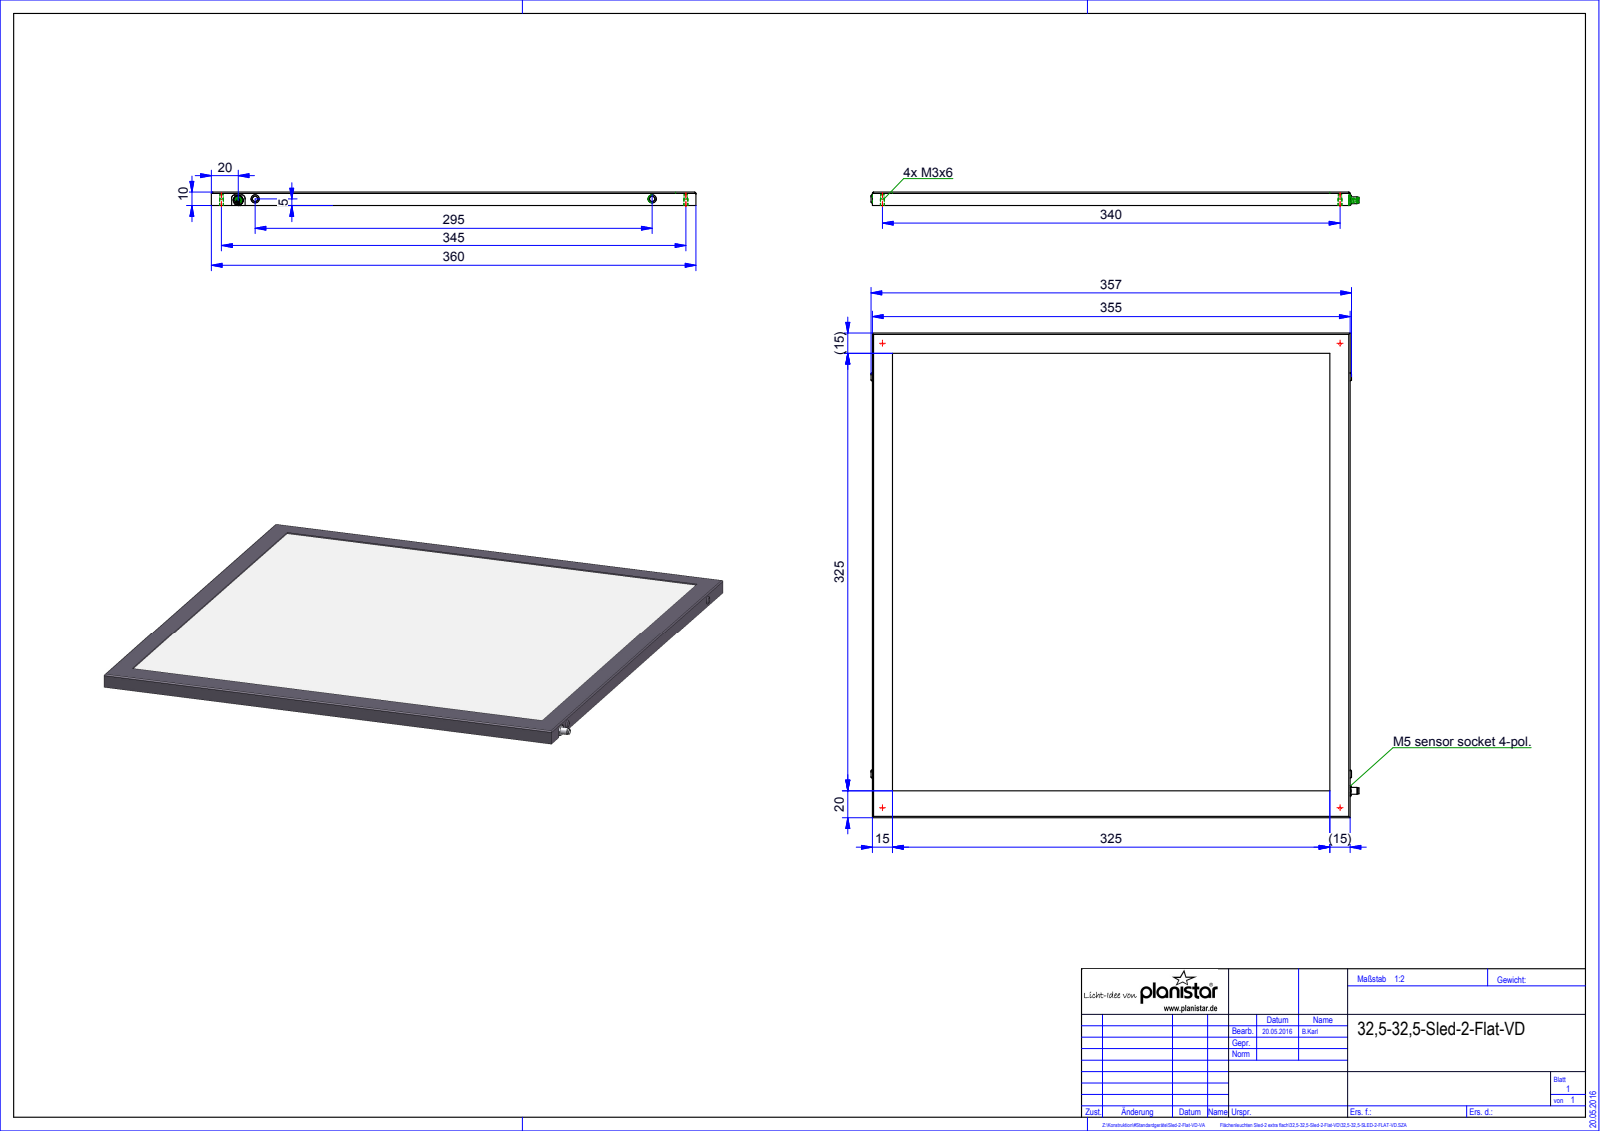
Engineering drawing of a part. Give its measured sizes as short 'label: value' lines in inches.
name: Root; Baugruppe_Xled-2-VD; Teil; QUADER_0
written by: HiCAD 2015 2002.1 Build 408 (AUTOMOTIVE_DESIGN)
unit: in
bodies: 4 solids, 99 faces (41 planar, 31 cylindrical, 27 other)
size: 14.28 × 14.173 × 0.394
volume: 71.52 in³; area: 420.5 in²
holes: 4× ⌀0.098, 4× ⌀0.118, 1× ⌀0.035, 1× ⌀0.126, 1× ⌀0.176
bosses: 4× ⌀0.019, 1× ⌀0.197, 1× ⌀0.169, 1× ⌀0.167
rounds: 4× R0.039, 2× R0.098, 1× R0.008, 1× R0.148
face distances: 0.354, 0.039, 0.394, 14.173, 13.976, 0.591, 13.386, 12.795, 13.583, 0.787
hole spacings: 13.386, 13.583, 19.07, 0.035
